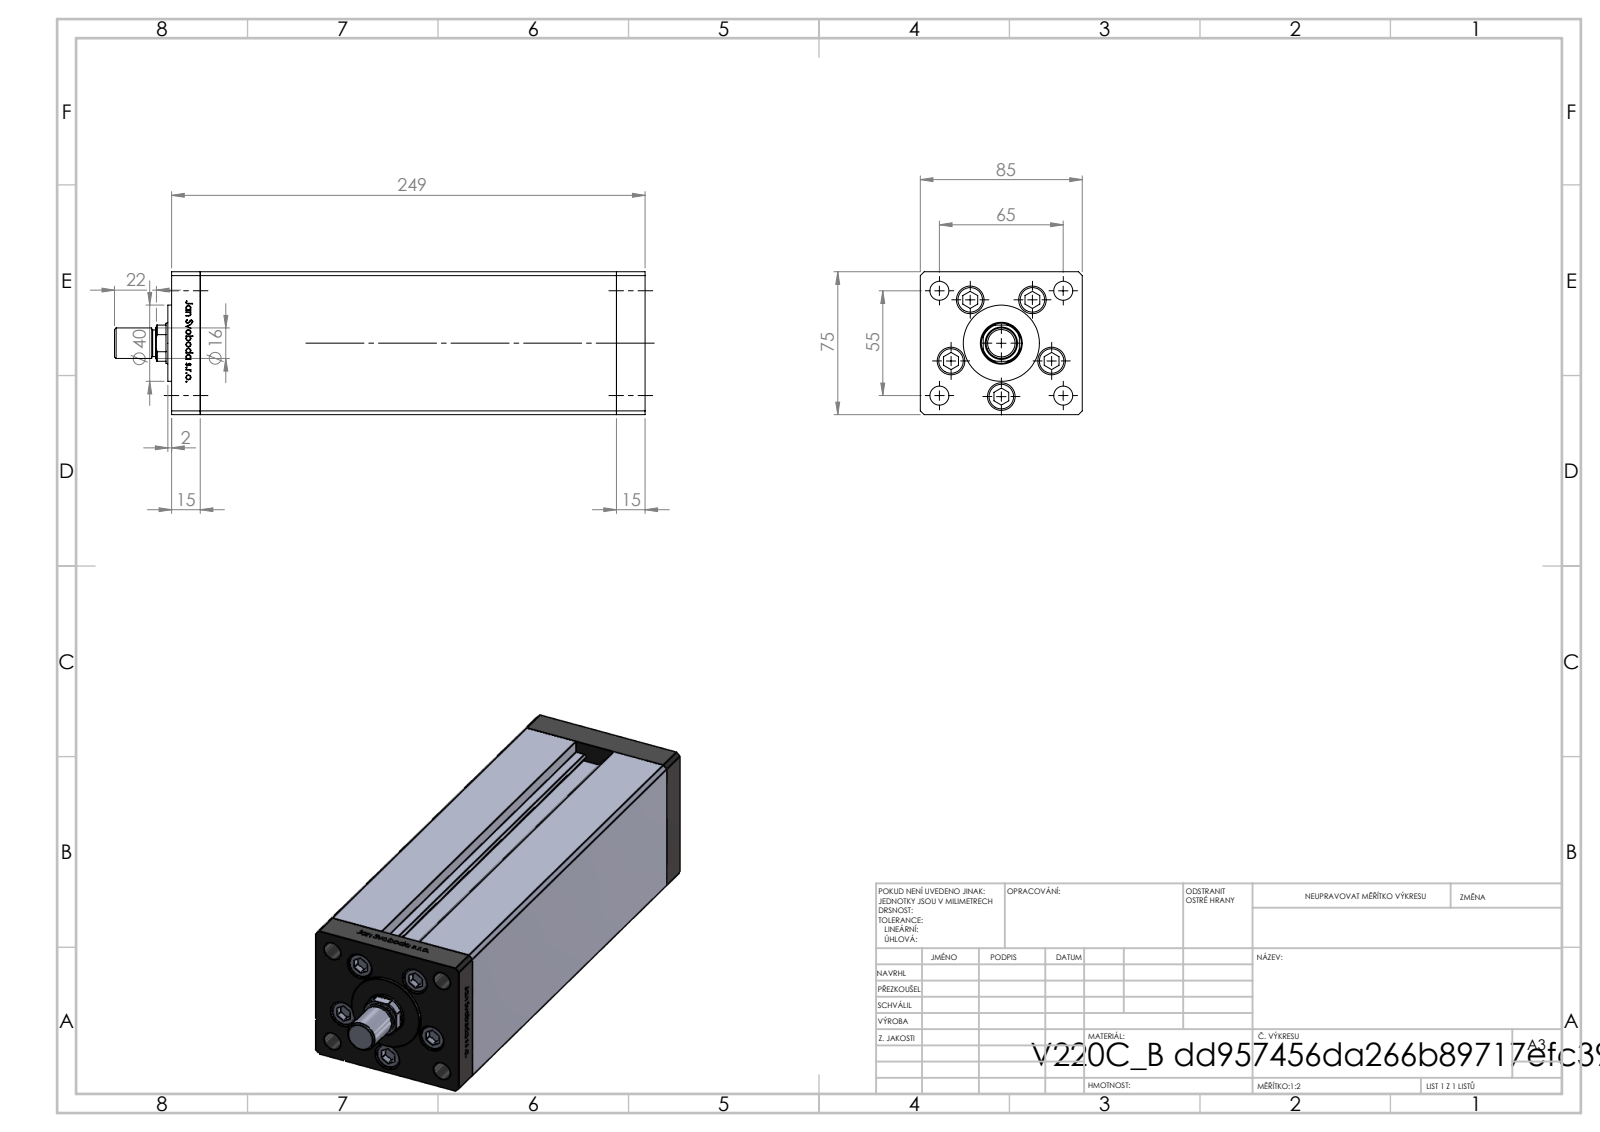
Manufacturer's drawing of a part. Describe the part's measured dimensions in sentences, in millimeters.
The part is named "V220C_FRONT_B; V220C_B_VC; V220C_B MIDDLE; V220C BACK_B (+2 more)". Its 3-D file was written by "SolidWorks 2019 (CONFIG_CONTROL_DESIGN)". It is 15 solids with 1191 faces: 466 planar, 147 cylindrical and 578 other. Overall it measures 278.5 by 85 by 75 millimeters. Its volume is 1 385 000 cubic millimeters and its surface area 197 194 square millimeters. Round holes: 5 of diameter 11, 5 of diameter 14.5, 4 of diameter 10, 2 of diameter 2, 2 of diameter 13.16, 1 of diameter 15, 1 of diameter 22. Round bosses or shafts: 5 of diameter 8, 1 of diameter 40, 1 of diameter 16, 1 of diameter 14. Partial cylindrical surfaces (rounded edges, fillets, slot ends): 2 of radius 0.93, 1 of radius 10.5. The main face-to-face distances are 85, 75, 218.5, 15, 233.5, 248.5, 68.5, 64.5, 10.5, 31.25. The hole center spacings are 28, 42.57, 16.86, 19.17, 32.33, 32.5, 33.63, 37.33.
